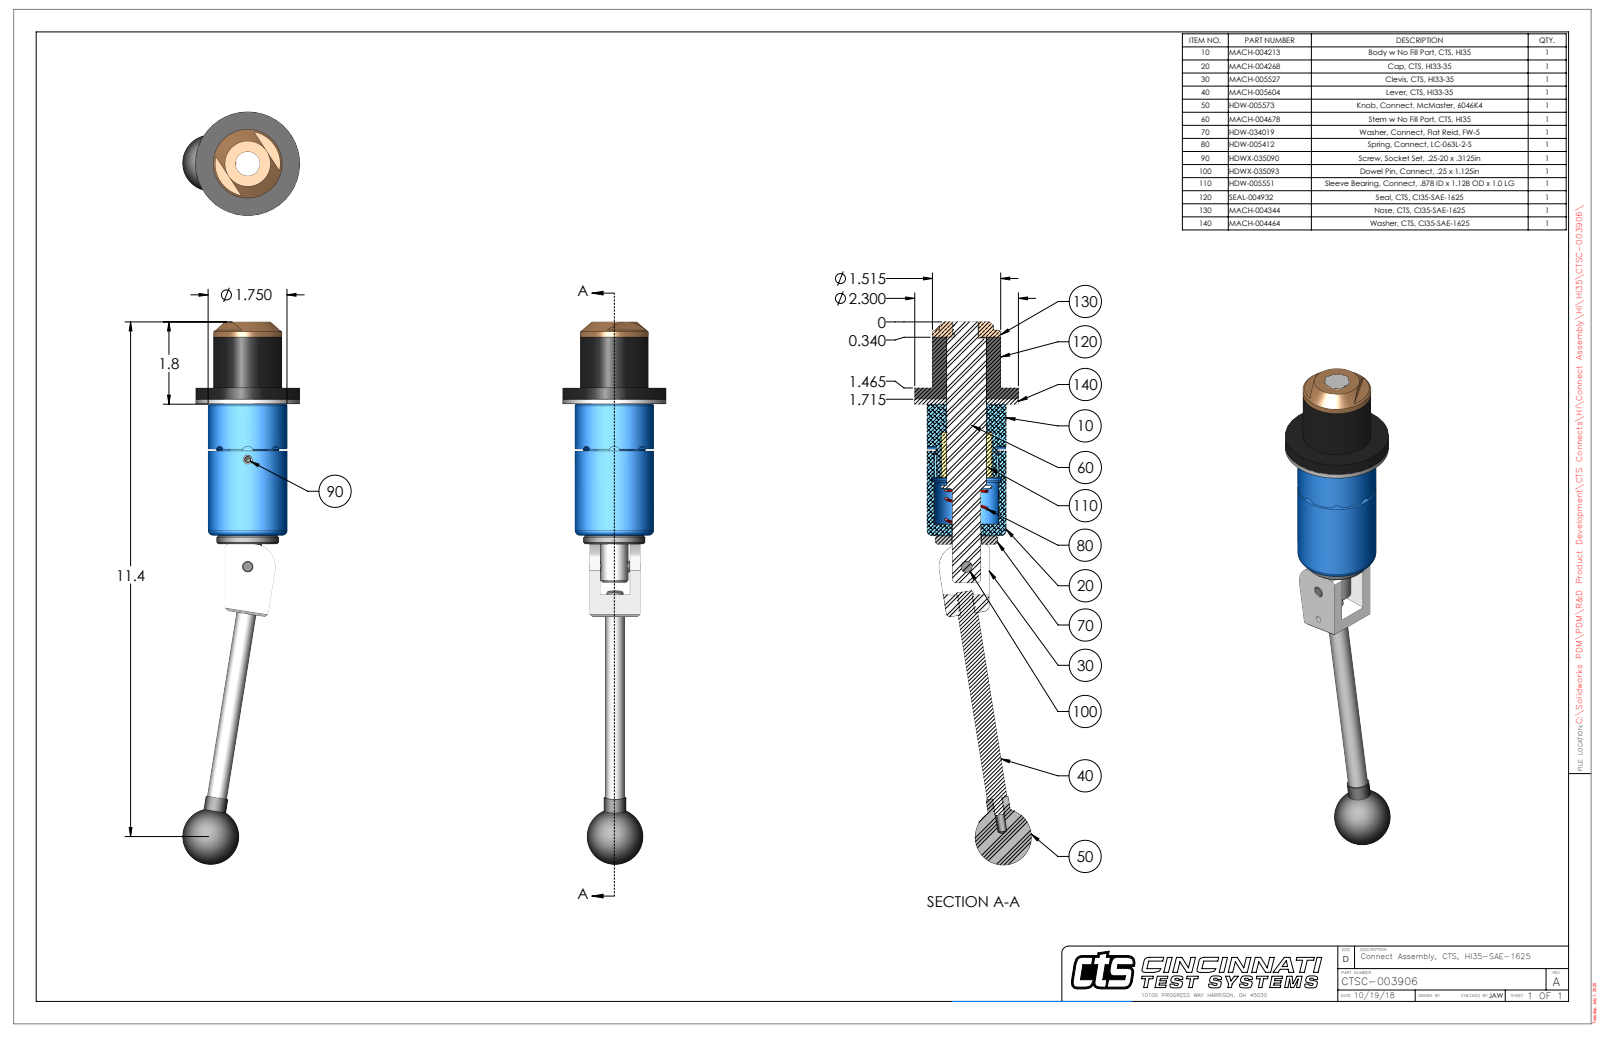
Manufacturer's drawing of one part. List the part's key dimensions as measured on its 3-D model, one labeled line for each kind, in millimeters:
Part name (STEP PRODUCT): CTSC-003906
STEP written by: SolidWorks 2023 (AUTOMOTIVE_DESIGN)
Units: millimetres
Bodies: 10 solids, 249 faces (91 planar, 100 cylindrical, 58 other)
Overall size (bounding box): 305.8 × 65.7 × 58.4
Volume: 232 500 mm³ · Surface area: 57 590 mm²
Round holes (diameter × count): ⌀5.1 ×2, ⌀3.8 ×1, ⌀6.3 ×1, ⌀6.4 ×1, ⌀8 ×1, ⌀13.5 ×1, ⌀16.1 ×1, ⌀16.7 ×1, ⌀22.3 ×1, ⌀22.4 ×1, ⌀22.5 ×1, ⌀36 ×1
Round bosses / shafts (diameter × count): ⌀6.4 ×2, ⌀58.4 ×1, ⌀44.5 ×1, ⌀38.5 ×1, ⌀38.5 ×1, ⌀35.1 ×1, ⌀22.1 ×1, ⌀22.1 ×1
Partial cylindrical surfaces — rounded edges, fillets, slot ends (radius × count): R3.2 ×4, R0.7 ×2, R12.7 ×1, R17.7 ×1, R20.5 ×1
Main face-to-face distances: 2.8, 34.9, 37.7, 111.8, 76.9, 74.1, 28.6, 6.4, 9.1, 83.2
Hole centre spacings: 18.8, 60.4, 79.1
